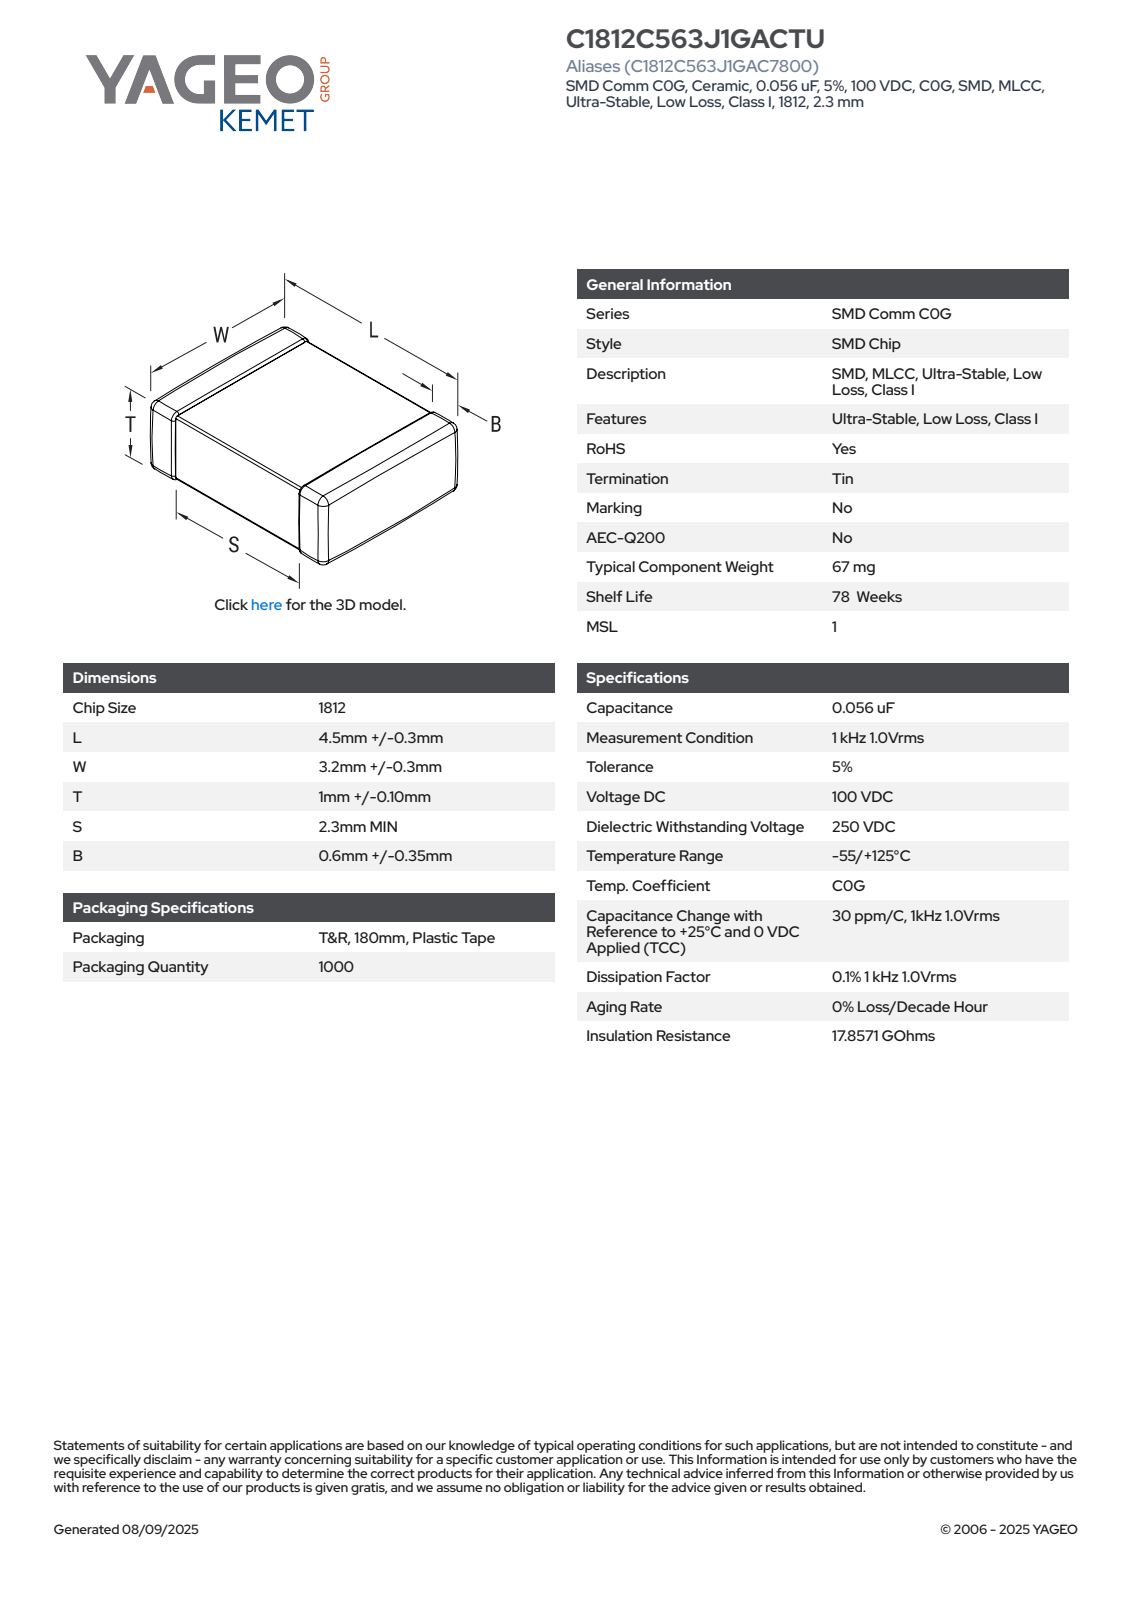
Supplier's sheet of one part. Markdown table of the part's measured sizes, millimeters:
| quantity | value |
| --- | --- |
| part name | CCS_CCSTDNOS_1812_L4.8W3.5T1.1B0.95 |
| STEP written by | SolidWorks 2014 (AUTOMOTIVE_DESIGN) |
| units | millimeters |
| bodies | 4 solids, 125 faces (71 planar, 38 cylindrical, 16 other) |
| overall size | 4.8 × 3.5 × 1.1 |
| volume | 17 mm³ |
| surface area | 50 mm² |
| main face-to-face distances | 1.03, 0.96, 1.1, 4.8, 3.43, 3.36, 3.5, 1.49, 0.34, 1.94 |
